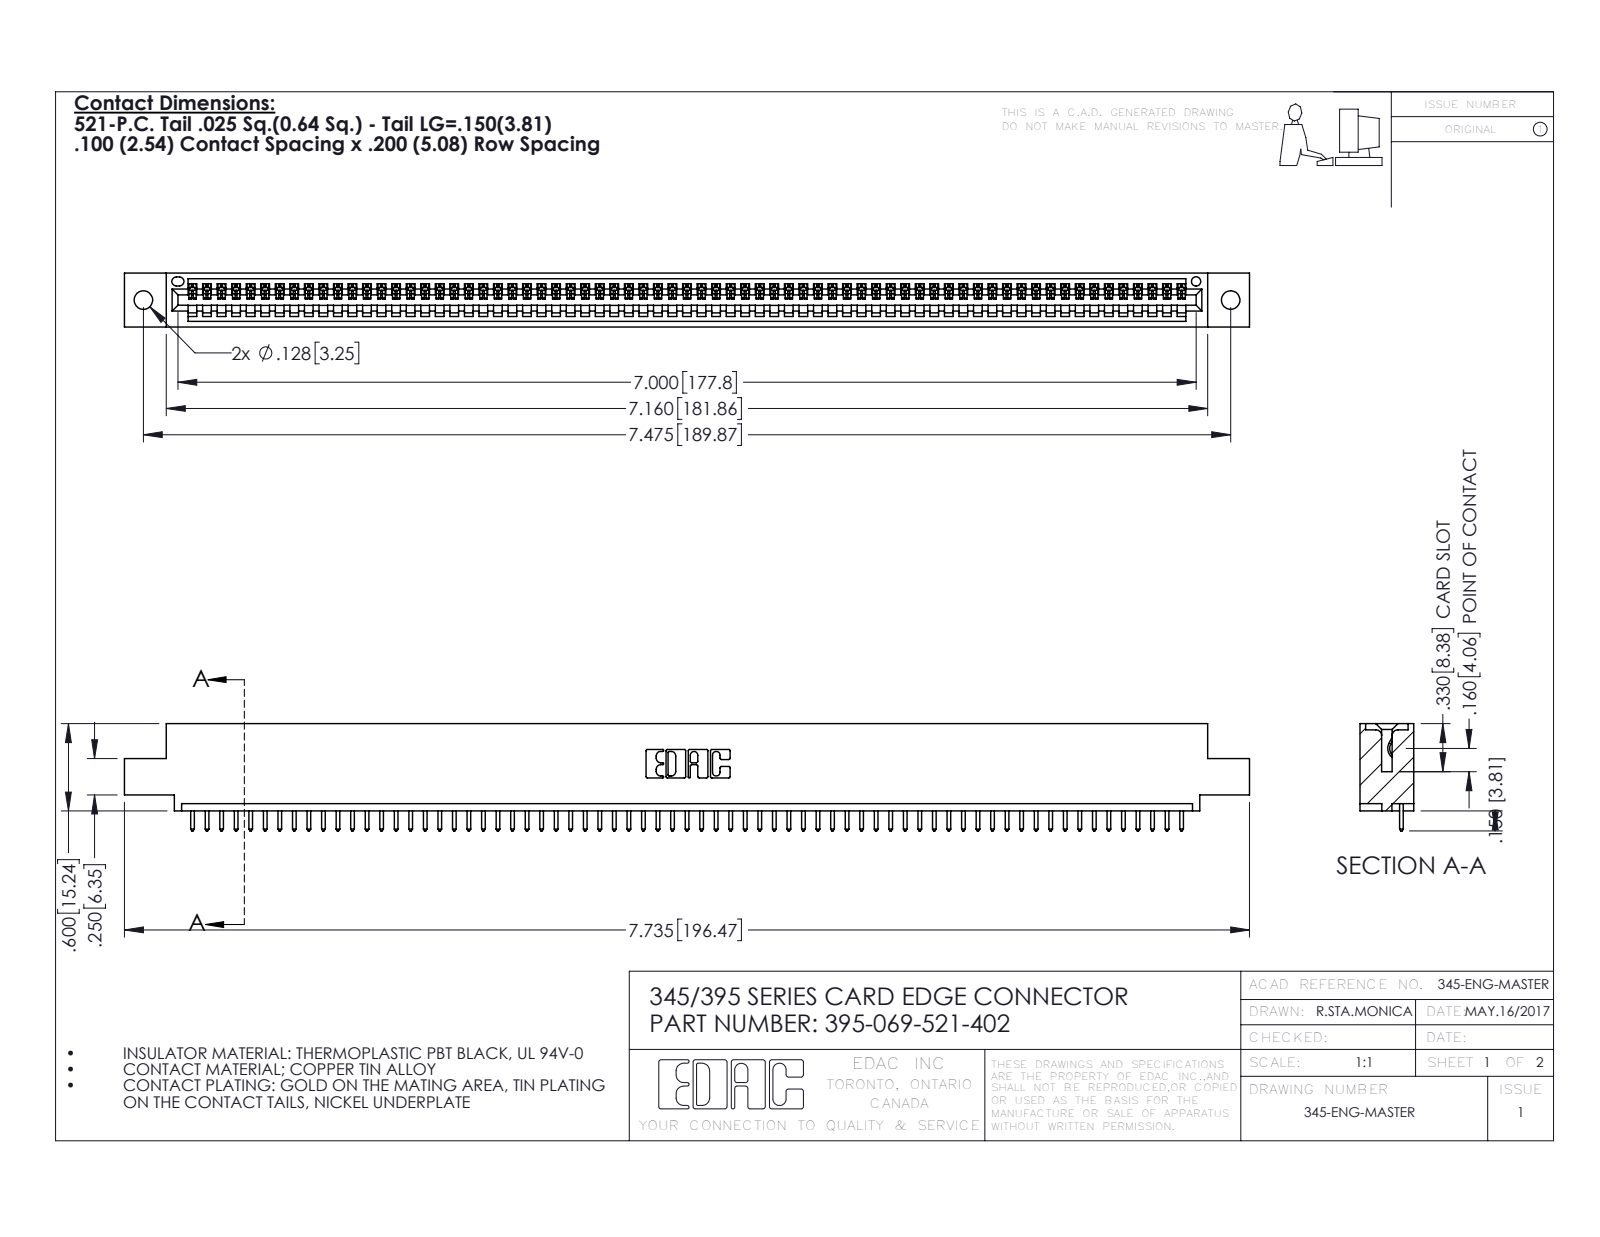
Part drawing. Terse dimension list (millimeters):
name: 345 Part_0.110 Offset - 0.128 Dia; 345-292-001_345-293-121; 395-069-521-402
written by: SolidWorks 2016 (CONFIG_CONTROL_DESIGN)
unit: mm
bodies: 70 solids, 4132 faces (2844 planar, 1288 cylindrical, 0 other)
size: 196.5 × 18.7 × 9.4
volume: 18 580 mm³; area: 24 100 mm²
holes: 2× ⌀3.3, 1× ⌀1.6
rounds: 138× R0.2, 138× R0.3, 22× R0.3, 6× R0.2, 6× R0.8, 3× R0.7, 2× R0.8, 2× R1
face distances: 7.6, 1.8, 9.4, 5.1, 2.5, 6.9, 0.6, 5.7, 3.8, 1.8
hole spacings: 6.9, 183.9, 189.9
